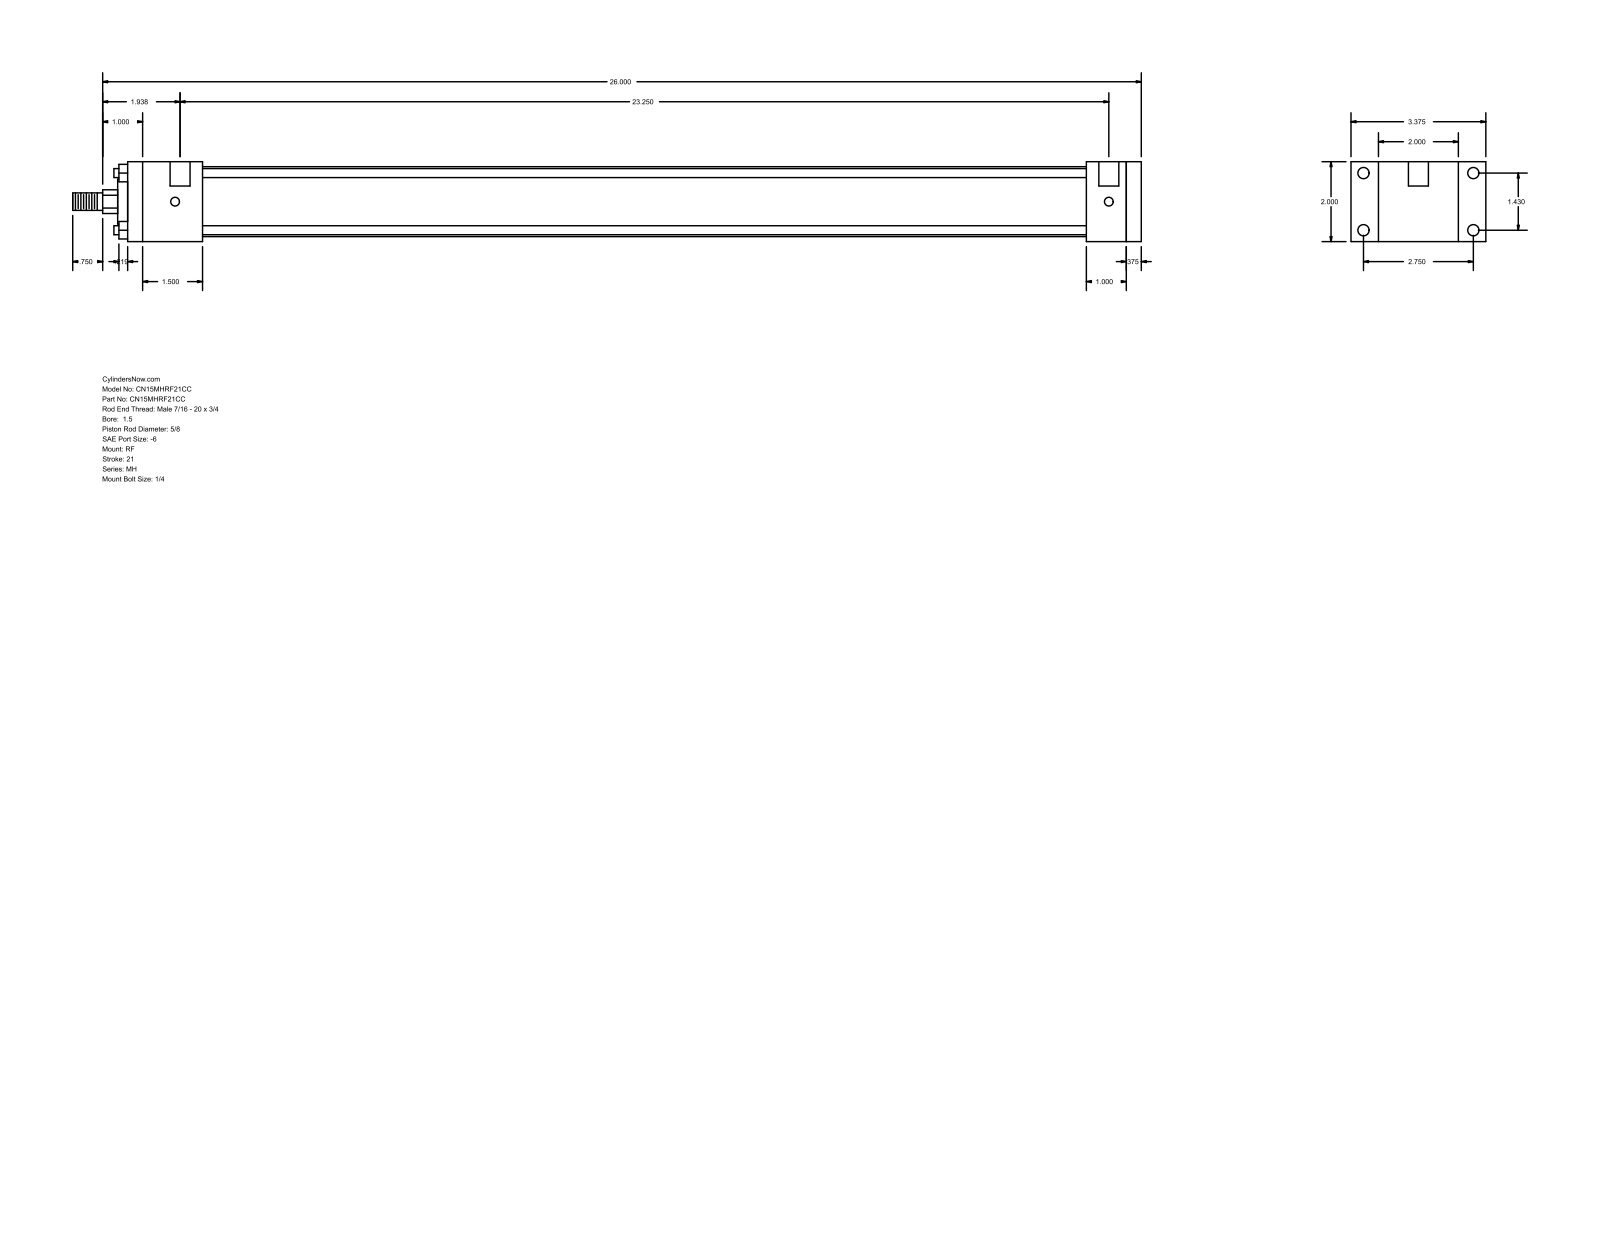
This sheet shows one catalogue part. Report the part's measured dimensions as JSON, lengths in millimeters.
{"part_name": "MH_RF__0150_0.625", "step_written_by": "GSSL Pune (CONFIG_CONTROL_DESIGN)", "units": "millimeters", "bodies": {"solids": 0, "faces": 92, "planar": 64, "cylindrical": 28, "other": 0}, "overall_size": [679.45, 85.72, 50.8], "round_holes": [[5.56, 4], [7.14, 4], [12.7, 2]], "round_bosses_or_shafts": [[5.71, 4], [44.45, 1], [28.57, 1], [15.88, 1], [11.11, 1]], "partial_cylinders_radius": [[7.54, 1]], "face_to_face_distances": [50.8, 9.52, 635, 644.52, 25.4, 17.46, 68.26, 609.6, 34.92, 47.62], "hole_center_spacings": [36.32, 69.84, 78.72, 593.72, 3.17, 590.55]}
